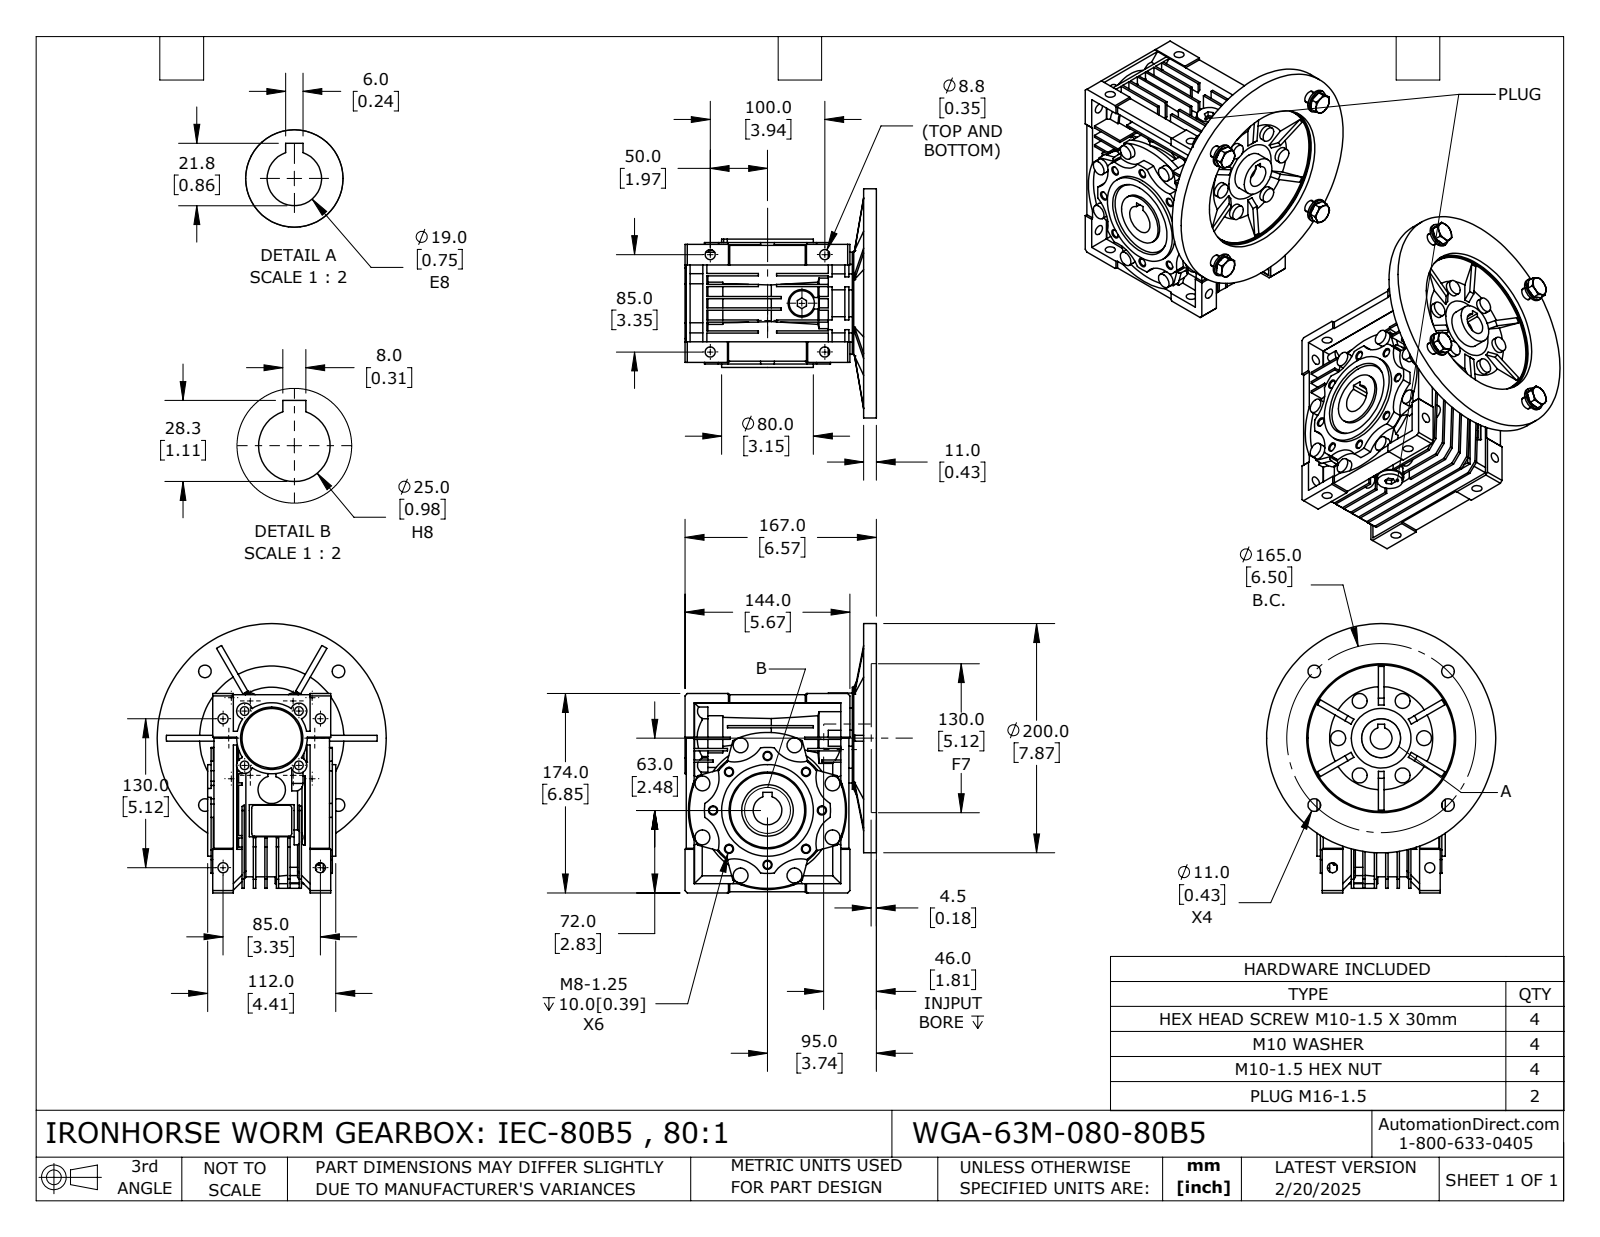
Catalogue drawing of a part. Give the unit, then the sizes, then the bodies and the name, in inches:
Units: inches
Overall size (bounding box): 9.252 × 7.874 × 7.222
Round holes (diameter × count): ⌀0.262 ×8, ⌀0.346 ×8, ⌀0.298 ×4, ⌀0.335 ×4, ⌀0.394 ×4, ⌀0.413 ×4, ⌀0.433 ×4, ⌀0.571 ×2, ⌀0.748 ×1, ⌀0.787 ×1, ⌀0.984 ×1, ⌀1.339 ×1
Round bosses / shafts (diameter × count): ⌀0.512 ×14, ⌀0.787 ×4, ⌀0.63 ×4, ⌀0.945 ×3, ⌀0.866 ×2, ⌀0.622 ×2, ⌀0.539 ×2, ⌀7.874 ×1
Partial cylindrical surfaces — rounded edges, fillets, slot ends (radius × count): R0.276 ×10, R1.063 ×8, R0.098 ×4, R0.329 ×1, R1.161 ×1, R1.201 ×1, R1.654 ×1, R1.811 ×1
Main face-to-face distances: 0.394, 0.315, 0.787, 0.079, 0.433, 1.181, 0.472, 0.276, 1.575, 0.709
Hole centre spacings: 1.431, 1.87, 2.645, 3.456, 3.506, 1.319, 1.865, 1.929
Volume: 124 in³ · Surface area: 622.2 in²
Bodies: 20 solids, 1529 faces (897 planar, 394 cylindrical, 238 other)
Part name (STEP PRODUCT): WGA-63M-080-80B5
STEP written by: SolidWorks 2024 (CONFIG_CONTROL_DESIGN)
